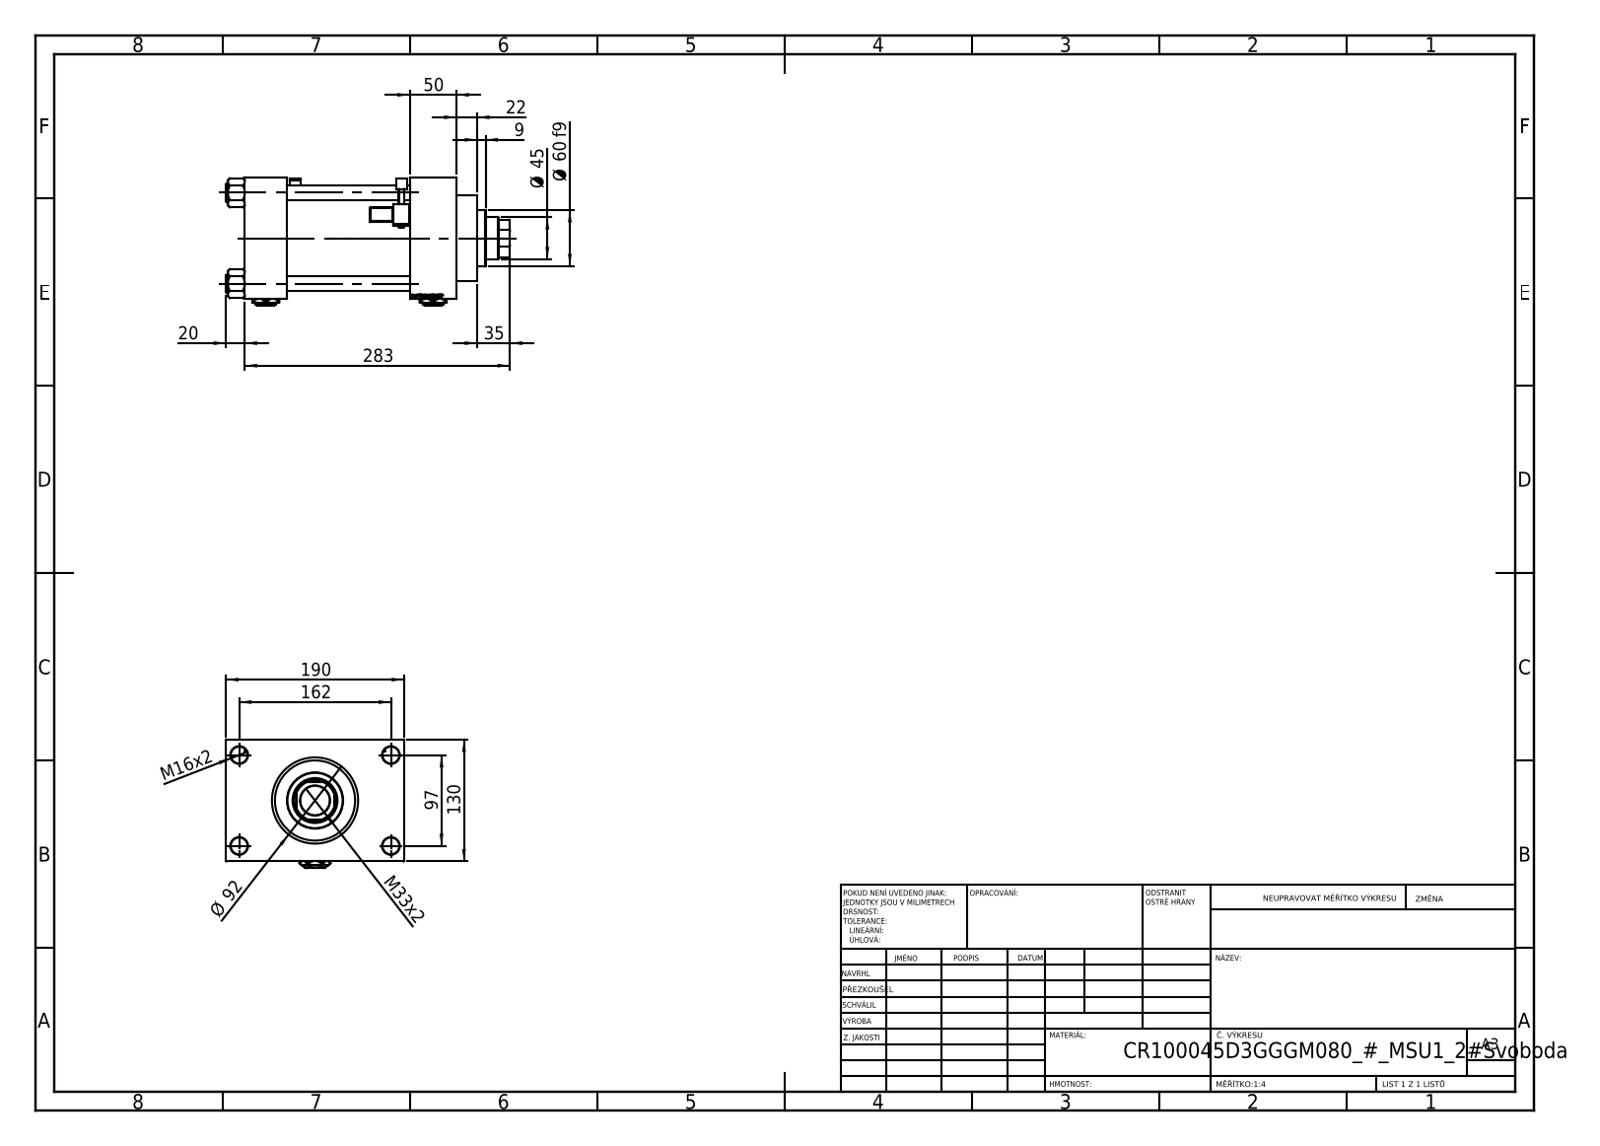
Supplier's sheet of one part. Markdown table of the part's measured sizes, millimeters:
| quantity | value |
| --- | --- |
| part name | V215CR_VCP_D; V215CR_D_TYCINKA; V215CR_MSU; NUT_M5_D (+3 more) |
| STEP written by | SolidWorks 2019 (CONFIG_CONTROL_DESIGN) |
| units | millimeters |
| bodies | 15 solids, 1407 faces (651 planar, 160 cylindrical, 596 other) |
| overall size | 303 × 190 × 137 |
| volume | 2 836 000 mm³ |
| surface area | 431 140 mm² |
| round holes (diameter × count) | 16 × 4, 18 × 4, 7 × 2, 26.44 × 2, 35 × 2, 31.5 × 1, 45 × 1, 48 × 1, 76 × 1, 85.5 × 1, 100 × 1 |
| round bosses / shafts (diameter × count) | 19 × 4, 6 × 2, 106 × 1, 92 × 1, 60 × 1 |
| partial cylindrical surfaces (radius × count) | 0.5 × 48, 1 × 2, 2.5 × 2, 4 × 2, 22 × 1 |
| main face-to-face distances | 130, 45, 131, 176, 226, 181, 50, 30, 160, 190 |
| hole center spacings | 32.55, 68.52, 94.41, 96.9, 102.27, 129.45, 161.73, 97 |
